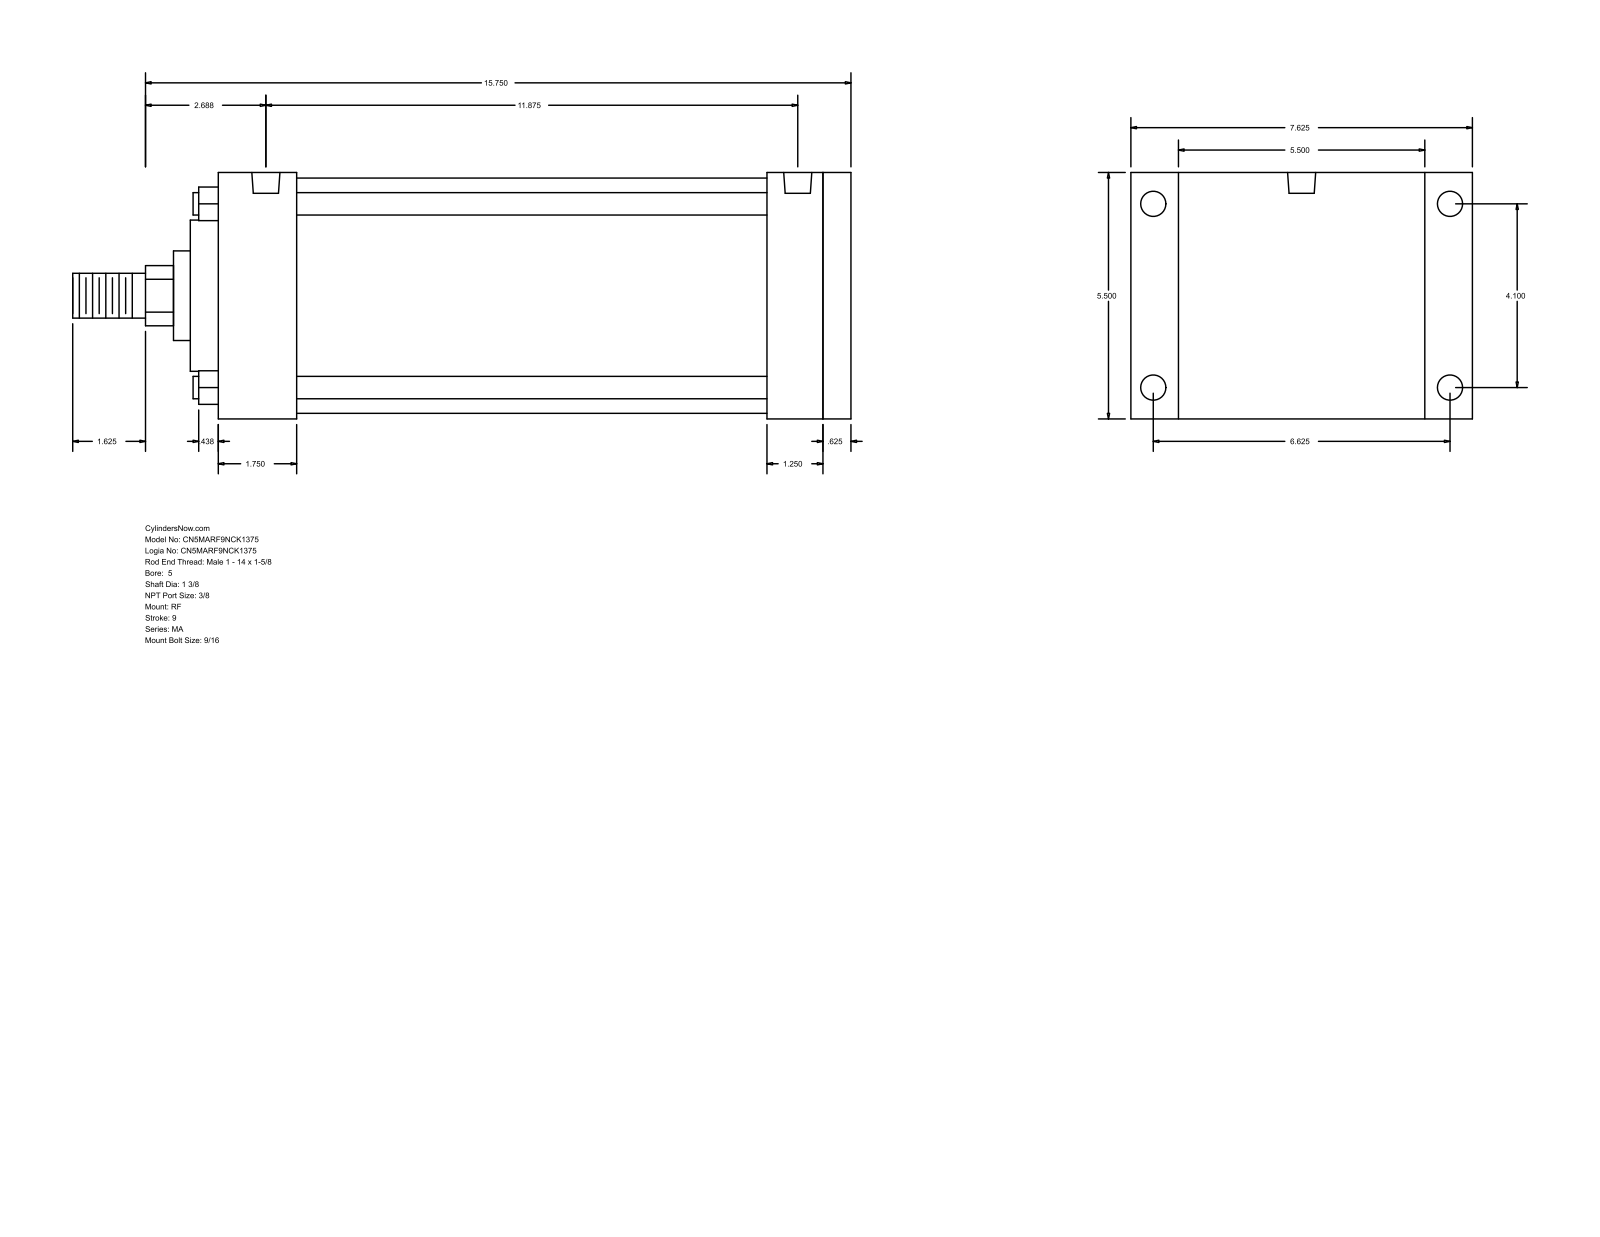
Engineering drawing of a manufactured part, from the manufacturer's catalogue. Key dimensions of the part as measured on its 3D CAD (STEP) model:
Part name (STEP PRODUCT): MA_RF__0500_1.375
STEP written by: GSSL Pune (CONFIG_CONTROL_DESIGN)
Units: millimetres
Bodies: 0 solids, 94 faces (65 planar, 29 cylindrical, 0 other)
Overall size (bounding box): 441.32 × 193.68 × 139.7
Round holes (diameter × count): ⌀11.11 ×4, ⌀14.29 ×4, ⌀15.93 ×2
Round bosses / shafts (diameter × count): ⌀12.7 ×4, ⌀133.35 ×1, ⌀85.72 ×1, ⌀50.8 ×1, ⌀34.92 ×1, ⌀25.4 ×1
Partial cylindrical surfaces — rounded edges, fillets, slot ends (radius × count): R17.06 ×1
Main face-to-face distances: 139.7, 358.78, 15.87, 342.91, 44.45, 298.46, 314.33, 311.16, 266.71, 31.75
Hole centre spacings: 4.77, 104.14, 168.28, 197.9, 292.09, 296.86, 301.63
